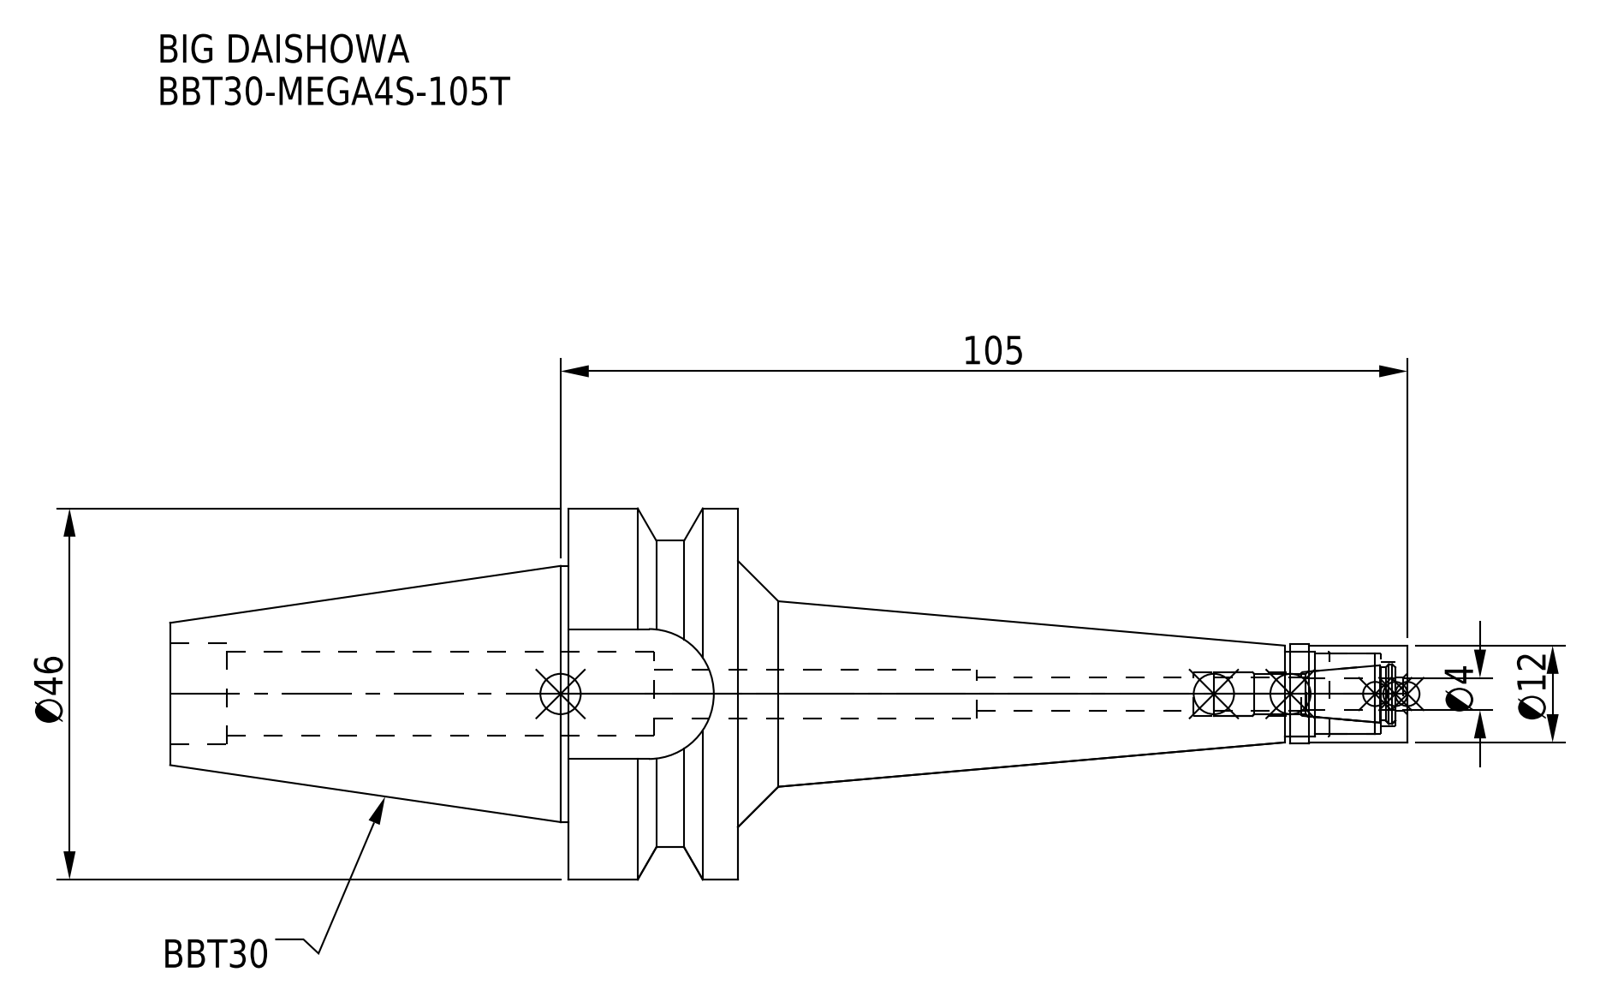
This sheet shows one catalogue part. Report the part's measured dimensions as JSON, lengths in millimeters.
{"part_name": "BBT30-MEGA4S-105T.stp; BBT30-MEGA4S-105T_1.stp; DXF_TEMP_ASSY_ASM_4_ASM.stp; BBT30-MEGA4S-105T-FreeParts (+3 more)", "step_written_by": "SolidWorks 2019 (CONFIG_CONTROL_DESIGN)", "units": "millimeters", "bodies": {"solids": 2, "faces": 74, "planar": 22, "cylindrical": 38, "other": 14}, "overall_size": [153.4, 46, 46], "volume_mm3": 66614, "surface_area_mm2": 18590, "round_holes": [[4.1, 1], [4.2, 1], [5.4, 1], [6, 1], [8, 1], [10, 1], [10.4, 1], [10.5, 1], [12.5, 1]], "round_bosses_or_shafts": [[46, 1], [31.75, 1], [12.3, 1], [12, 1]], "partial_cylinders_radius": [[8.05, 1], [19, 1]], "face_to_face_distances": [21, 32.6, 49.4, 70.4, 16.1, 83, 104, 153.4, 0.7, 93.4]}
